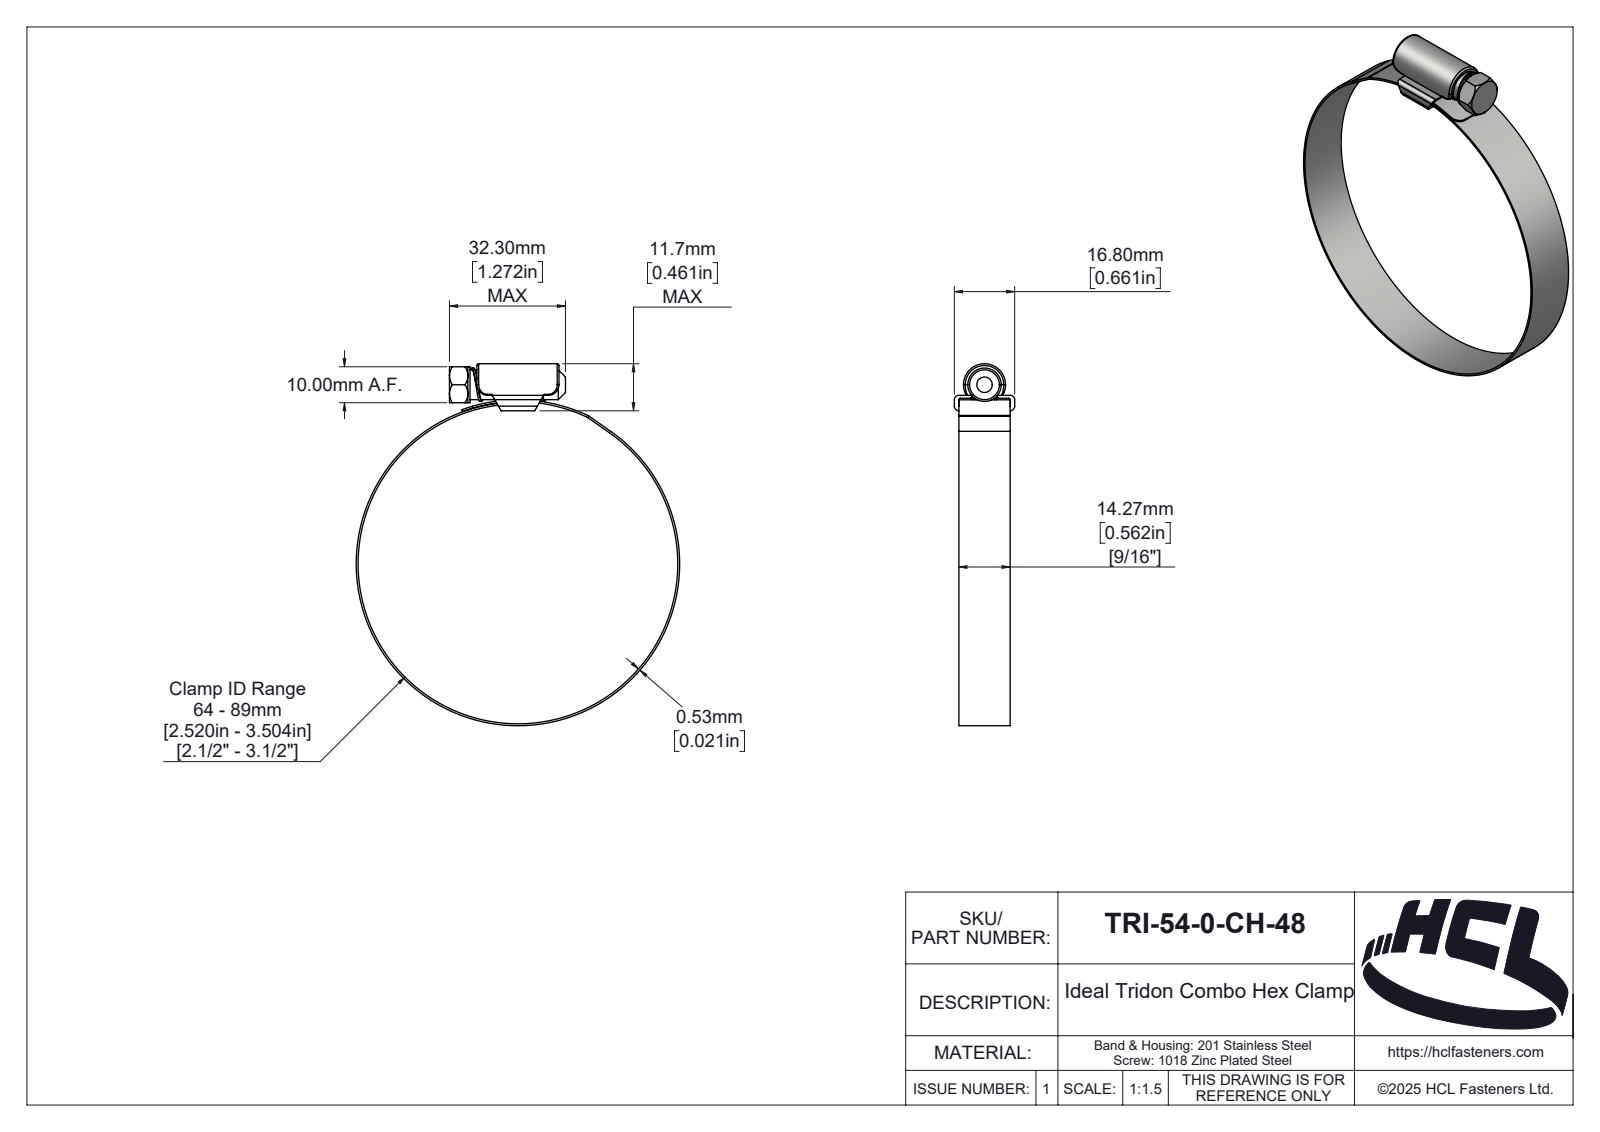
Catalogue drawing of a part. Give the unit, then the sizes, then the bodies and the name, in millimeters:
Units: millimetres
Overall size (bounding box): 100.73 × 90.06 × 16.8
Round holes (diameter × count): ⌀89 ×1
Round bosses / shafts (diameter × count): ⌀90.06 ×1, ⌀10 ×1, ⌀8.3 ×1
Partial cylindrical surfaces — rounded edges, fillets, slot ends (radius × count): R0.5 ×6, R3 ×4, R0.1 ×2, R1.2 ×2, R1.3 ×2, R0.46 ×1, R1.89 ×1, R2 ×1
Main face-to-face distances: 1.2, 14.26, 0.53, 3.5, 2.3, 4.3, 3.1, 0.8, 9.99, 1.27
Volume: 5 135 mm³ · Surface area: 11 788 mm²
Bodies: 3 solids, 212 faces (35 planar, 101 cylindrical, 76 other)
Part name (STEP PRODUCT): TRI-54-0-CH-48
STEP written by: SolidWorks 2025 (AUTOMOTIVE_DESIGN)
